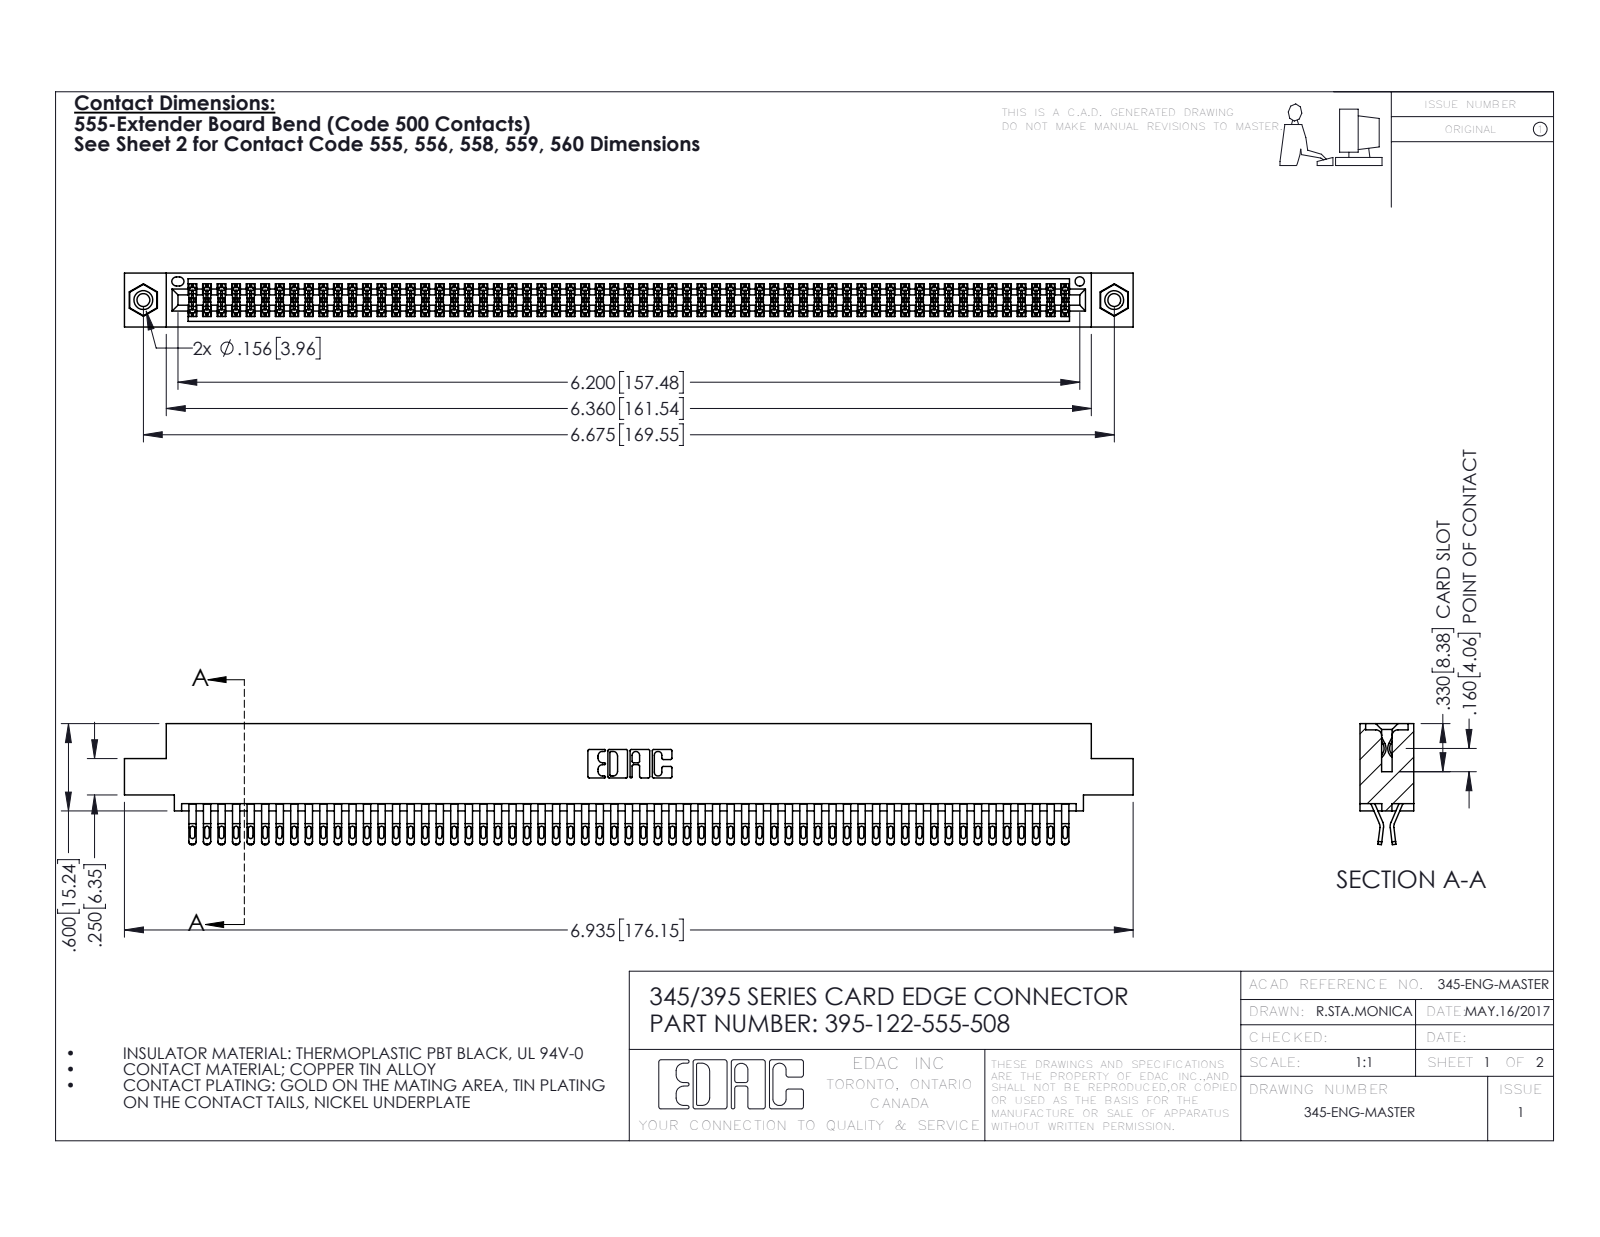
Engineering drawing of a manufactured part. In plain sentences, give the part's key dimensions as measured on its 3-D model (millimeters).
The part is named "345-292-001_555 Tail; 345 Part_0.110 Offset - 0.156 Dia-TI; 345-250-001_345-250-003-102; 395-122-555-508". Its 3-D file was written by "SolidWorks 2016 (CONFIG_CONTROL_DESIGN)". It is 125 solids with 7022 faces: 3898 planar, 3108 cylindrical and 16 other. Overall it measures 176.1 by 21.1 by 9.4 millimeters. Its volume is 17 570 cubic millimeters and its surface area 27 660 square millimeters. Round holes: 2 of diameter 2.3, 2 of diameter 3.2, 2 of diameter 4, 1 of diameter 1.6. Round bosses or shafts: 2 of diameter 3.9. Partial cylindrical surfaces (rounded edges, fillets, slot ends): 305 of radius 0.4, 244 of radius 0.5, 183 of radius 0.2, 22 of radius 0.3, 6 of radius 0.2, 6 of radius 0.8, 3 of radius 0.7, 2 of radius 0.3. The main face-to-face distances are 1.8, 7.6, 0.6, 9.4, 5.1, 2.5, 6.9, 5.7, 4.4, 3.8. The hole center spacings are 6.9, 163.6, 169.5.
